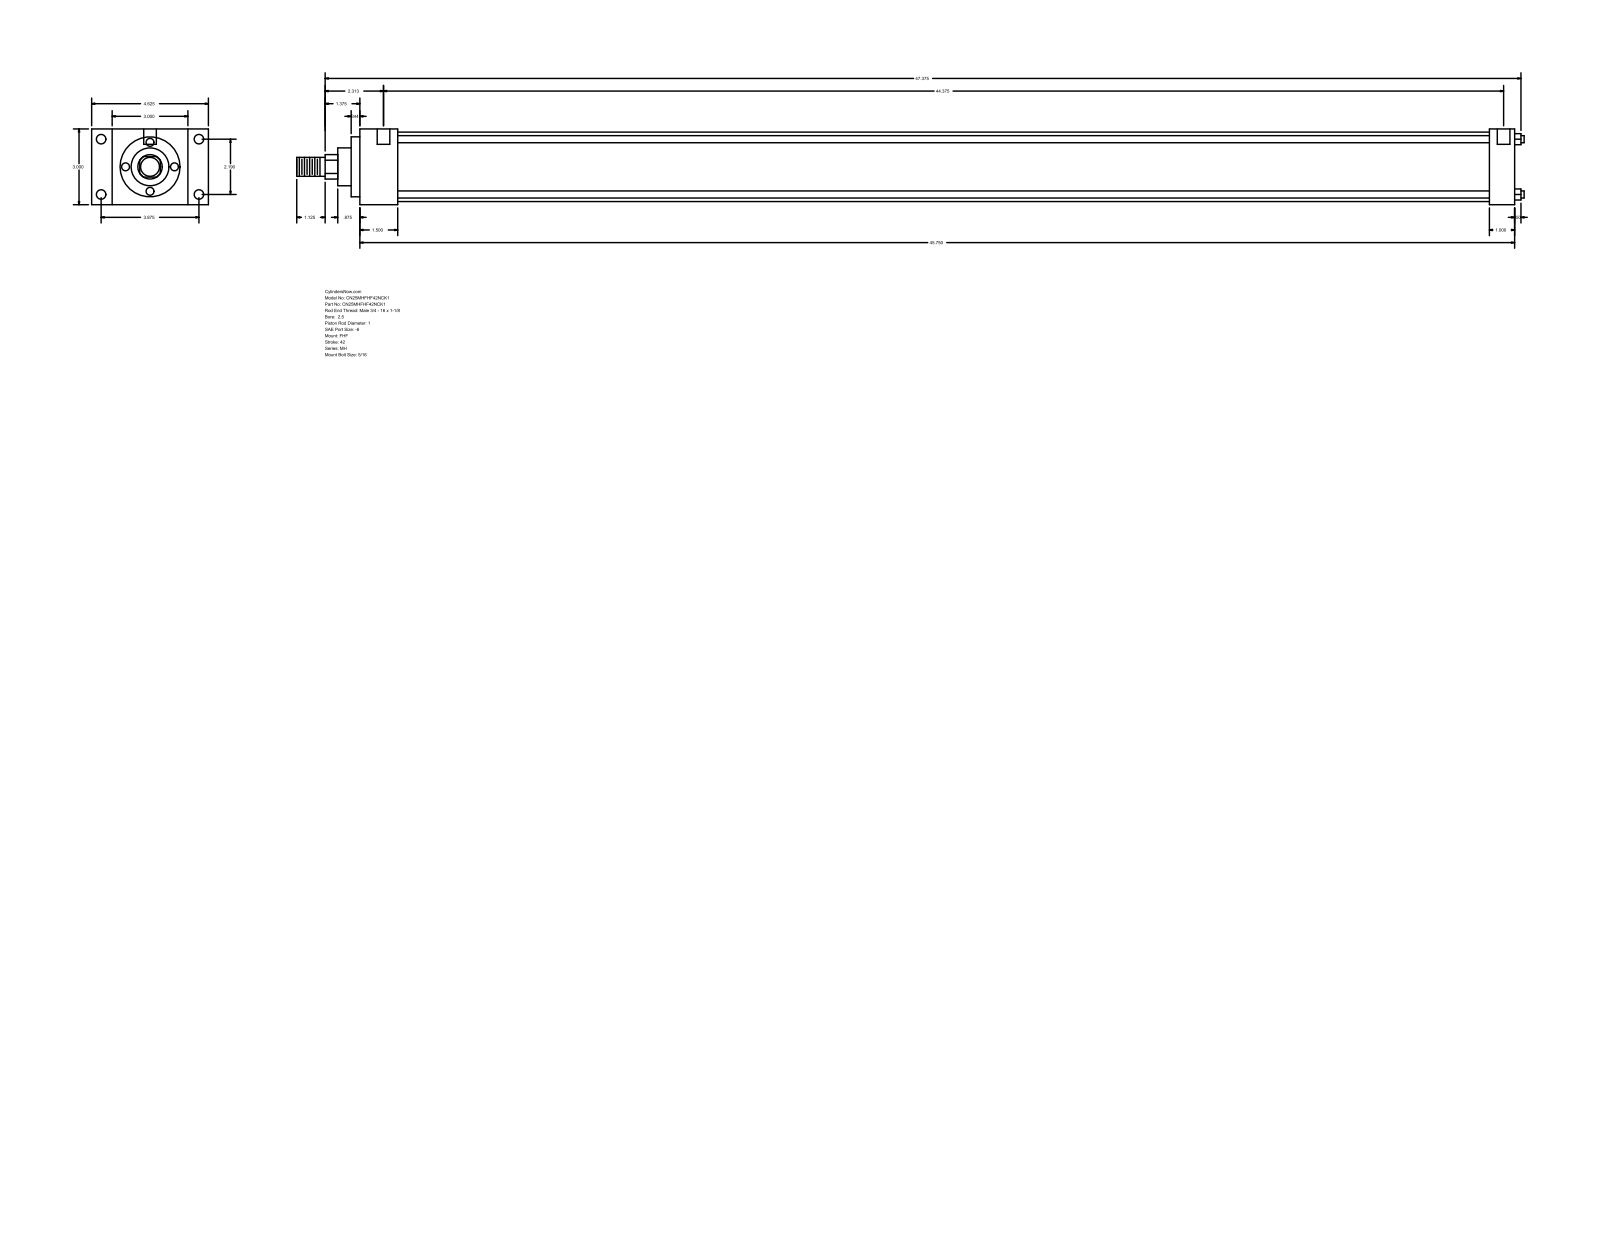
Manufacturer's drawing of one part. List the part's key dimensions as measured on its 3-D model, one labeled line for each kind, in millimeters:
Part name (STEP PRODUCT): MH_FHF__0250_1
STEP written by: GSSL Pune (CONFIG_CONTROL_DESIGN)
Units: millimetres
Bodies: 0 solids, 90 faces (61 planar, 29 cylindrical, 0 other)
Overall size (bounding box): 1235.08 × 117.47 × 76.2
Round holes (diameter × count): ⌀5.56 ×4, ⌀9.53 ×4, ⌀12.7 ×2
Round bosses / shafts (diameter × count): ⌀7.14 ×4, ⌀69.85 ×1, ⌀60.33 ×1, ⌀38.1 ×1, ⌀25.4 ×1, ⌀19.05 ×1
Partial cylindrical surfaces — rounded edges, fillets, slot ends (radius × count): R12.29 ×1
Main face-to-face distances: 76.2, 1162.05, 38.11, 1123.94, 20.64, 96.84, 117.48, 25.39, 1136.66, 1098.55
Hole centre spacings: 55.62, 98.42, 113.05, 1135.06, 3.18, 4.76, 1127.12, 1130.3
